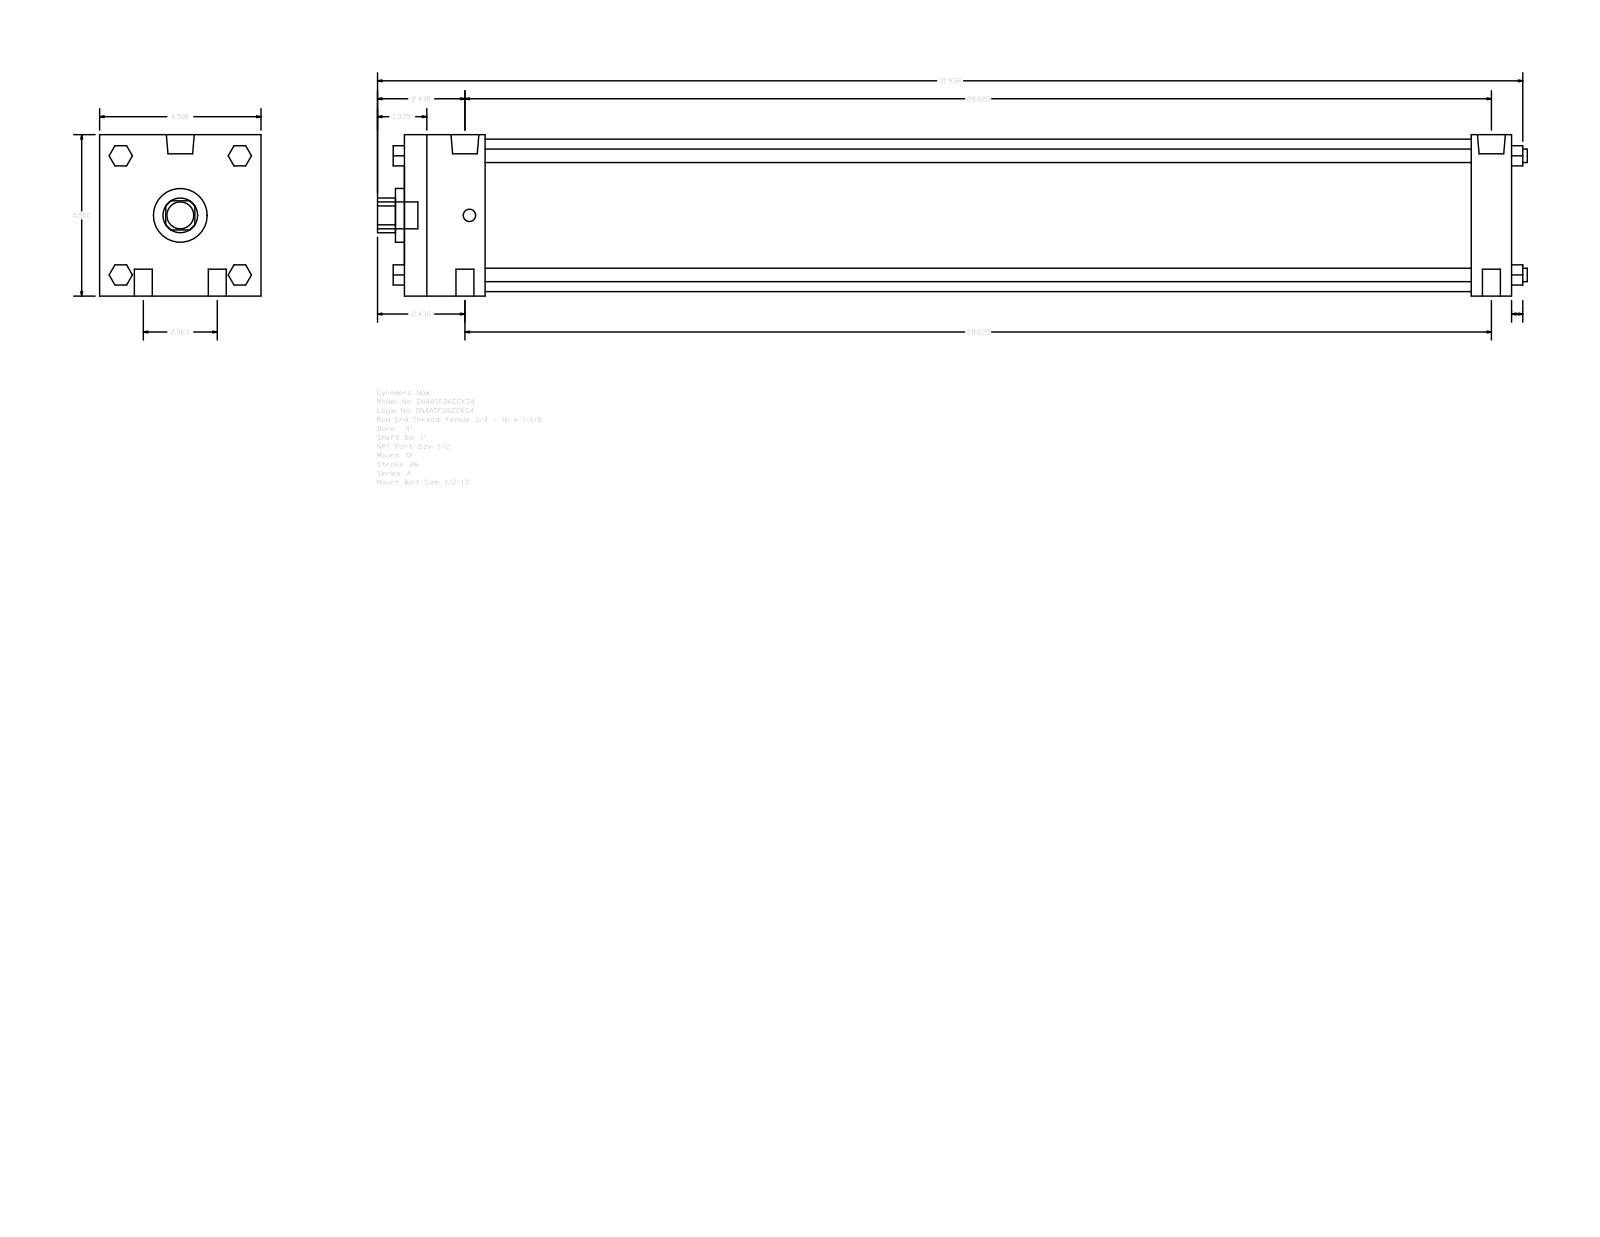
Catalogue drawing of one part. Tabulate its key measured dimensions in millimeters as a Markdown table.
| quantity | value |
| --- | --- |
| part name | A_SF__0400_1 |
| STEP written by | GSSL Pune (CONFIG_CONTROL_DESIGN) |
| units | millimeters |
| bodies | 0 solids, 124 faces (94 planar, 30 cylindrical, 0 other) |
| overall size | 814.39 × 114.3 × 114.3 |
| round holes (diameter × count) | 25.4 × 1, 38.1 × 1, 107.95 × 1 |
| round bosses / shafts (diameter × count) | 12.7 × 4, 9.53 × 4, 19.77 × 2, 8.73 × 2, 19.05 × 1 |
| partial cylindrical surfaces (radius × count) | 12.29 × 1 |
| main face-to-face distances | 114.3, 784.22, 28.57, 755.65, 57.15, 698.5, 727.07, 14.29, 42.16, 73.03 |
